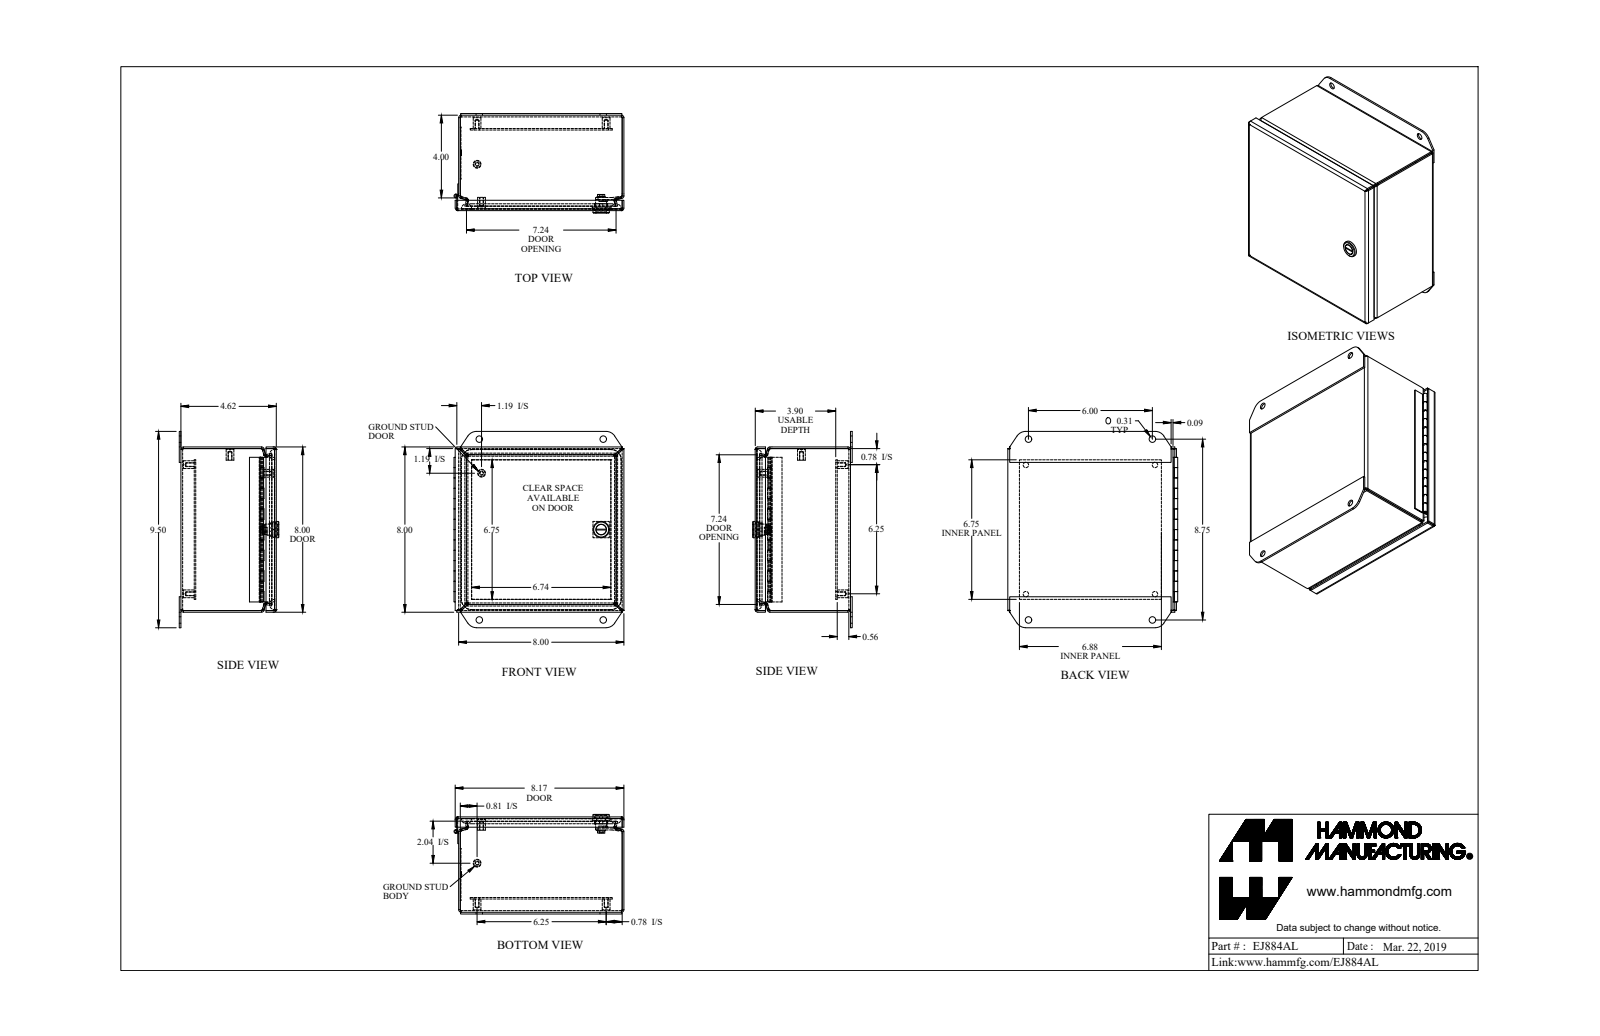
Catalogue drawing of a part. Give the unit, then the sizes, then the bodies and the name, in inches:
Units: inches
Overall size (bounding box): 9.5 × 8.226 × 4.82
Round holes (diameter × count): ⌀0.159 ×6, ⌀0.265 ×4, ⌀0.313 ×4, ⌀0.516 ×1
Round bosses / shafts (diameter × count): ⌀0.375 ×6, ⌀0.33 ×6, ⌀0.788 ×1, ⌀0.535 ×1, ⌀0.496 ×1, ⌀0.435 ×1, ⌀0.18 ×1, ⌀0.1 ×1
Partial cylindrical surfaces — rounded edges, fillets, slot ends (radius × count): R0.041 ×16, R0.121 ×16, R0.281 ×12, R0.25 ×4, R0.499 ×4, R0.5 ×4, R0.06 ×2, R0.03 ×1
Main face-to-face distances: 0.081, 4.536, 7.919, 4.617, 8, 7.838, 4.455, 0.562, 0.643, 3.974
Hole centre spacings: 6.25, 8.839, 0.024, 1.256, 6.267, 7.502, 3.133, 4.376
Volume: 31.81 in³ · Surface area: 812.3 in²
Bodies: 14 solids, 586 faces (364 planar, 154 cylindrical, 68 other)
Part name (STEP PRODUCT): EJ884AL_Default
STEP written by: SolidWorks 2019 (CONFIG_CONTROL_DESIGN)
